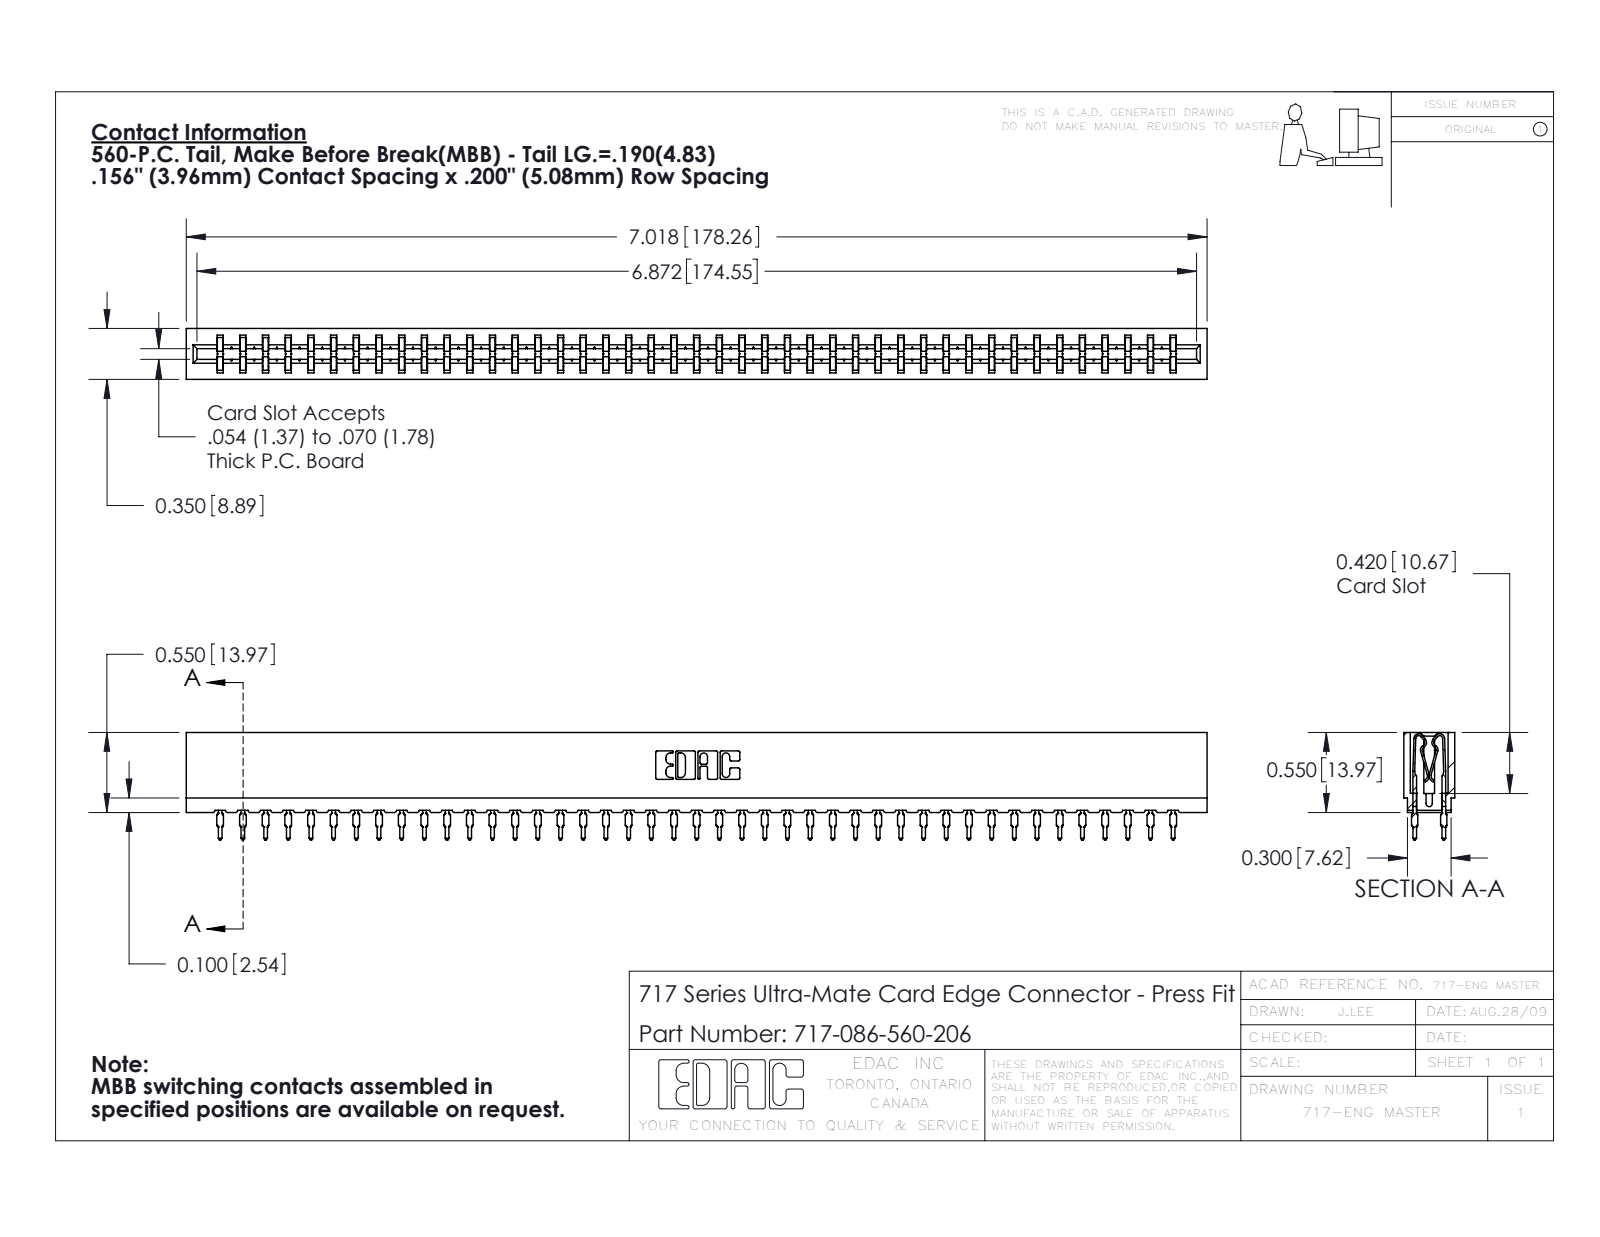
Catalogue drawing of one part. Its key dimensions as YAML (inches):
part_name: "745-292-001_560; 717 Part_Insulator Option - 06; 717-086-560-206"
step_written_by: "SolidWorks 2016 (CONFIG_CONTROL_DESIGN)"
units: inches
bodies: {solids: 87, faces: 8608, planar: 4483, cylindrical: 1889, other: 2236}
overall_size: [7.018, 0.739, 0.35]
volume: 0.962
surface_area: 39.73
partial_cylinders:
  - {radius: 0.021, count: 172}
  - {radius: 0.015, count: 86}
  - {radius: 0.01, count: 22}
  - {radius: 0.005, count: 8}
  - {radius: 0.011, count: 8}
  - {radius: 0.007, count: 6}
  - {radius: 0.031, count: 6}
  - {radius: 0.026, count: 3}
face_to_face_distances: [0.212, 0.138, 0.35, 0.063, 0.287, 0.076, 0.149, 0.074, 0.045, 0.305]
